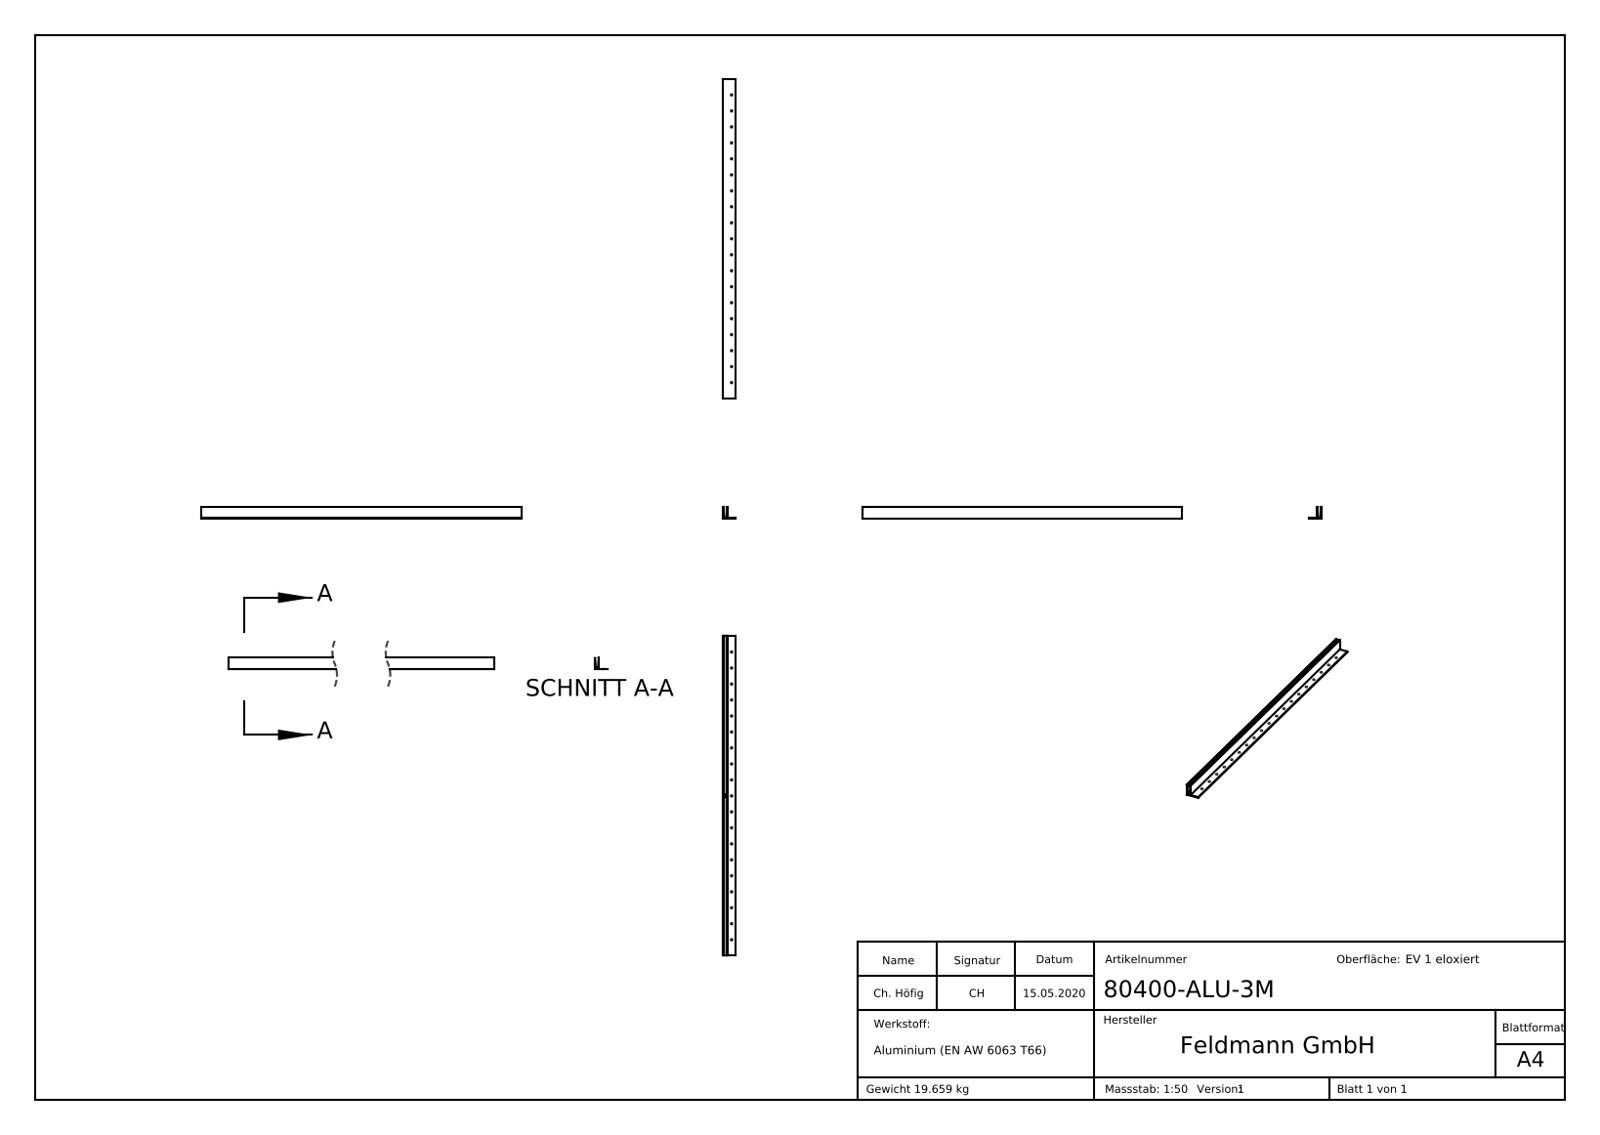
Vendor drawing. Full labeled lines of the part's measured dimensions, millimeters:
Part name (STEP PRODUCT): 80400-ALU-3M
STEP written by: SolidWorks 2015 (CONFIG_CONTROL_DESIGN)
Units: millimetres
Bodies: 1 solid, 316 faces (159 planar, 44 cylindrical, 113 other)
Overall size (bounding box): 3000 × 121 × 110
Volume: 7 281 000 mm³ · Surface area: 1 978 000 mm²
Round holes (diameter × count): ⌀12 ×19
Partial cylindrical surfaces — rounded edges, fillets, slot ends (radius × count): R1 ×3, R0.65 ×2
Main face-to-face distances: 41, 8, 9, 32, 6.2, 34.8, 25.8, 2.8, 23, 110
Hole centre spacings: 150, 300, 450, 600, 750, 900, 1050, 1200
